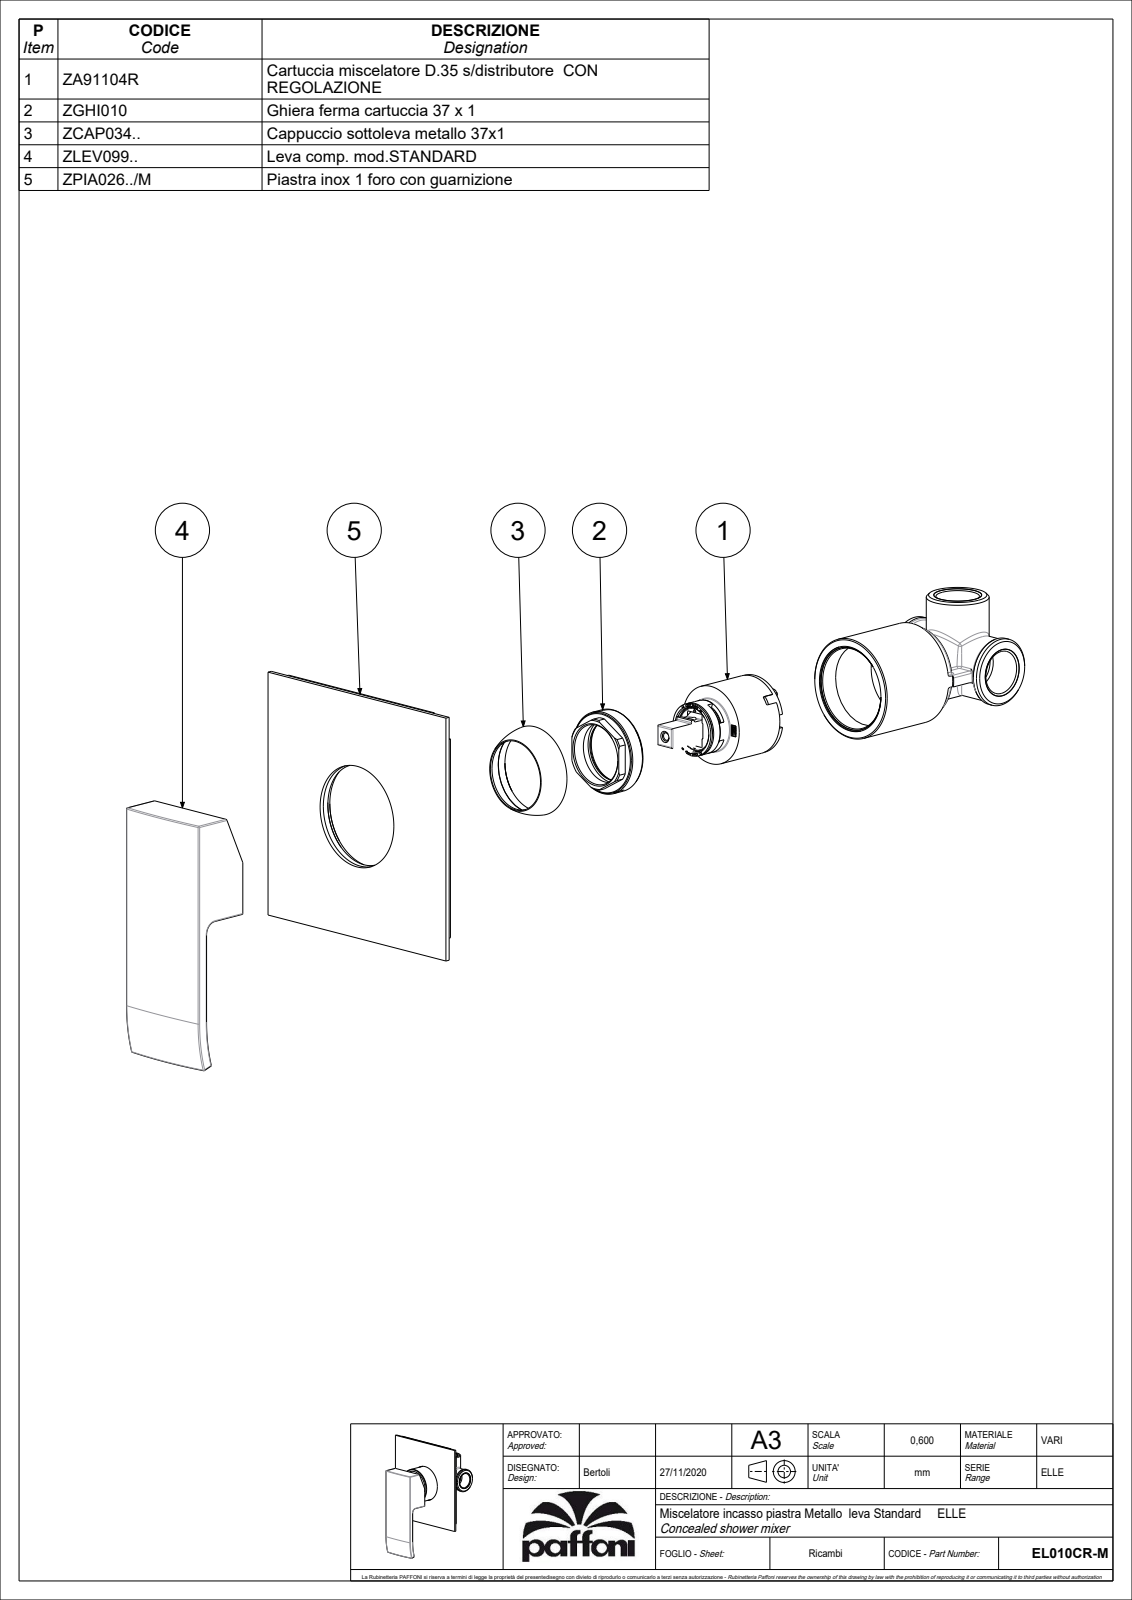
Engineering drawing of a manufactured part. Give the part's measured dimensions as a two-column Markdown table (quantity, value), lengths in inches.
| quantity | value |
| --- | --- |
| part name | EL010CRM |
| STEP written by | CREO PARAMETRIC BY PTC INC, 2020044 (CONFIG_CONTROL_DESIGN) |
| units | inches |
| bodies | 1 solid, 132 faces (42 planar, 50 cylindrical, 40 other) |
| overall size | 5.672 × 4.331 × 2.091 |
| volume | 6.275 in³ |
| surface area | 73.78 in² |
| round holes (diameter × count) | 0.118 × 1, 0.217 × 1, 0.307 × 1 |
| round bosses / shafts (diameter × count) | 1.764 × 1, 0.299 × 1, 0.197 × 1 |
| partial cylindrical surfaces (radius × count) | 0.059 × 14, 0.02 × 10, 0.079 × 4, 11.811 × 2 |
| main face-to-face distances | 0.079, 1.772, 1.98, 1.902, 1.28, 3.051, 1.378, 1.299, 0.602, 1.076 |
